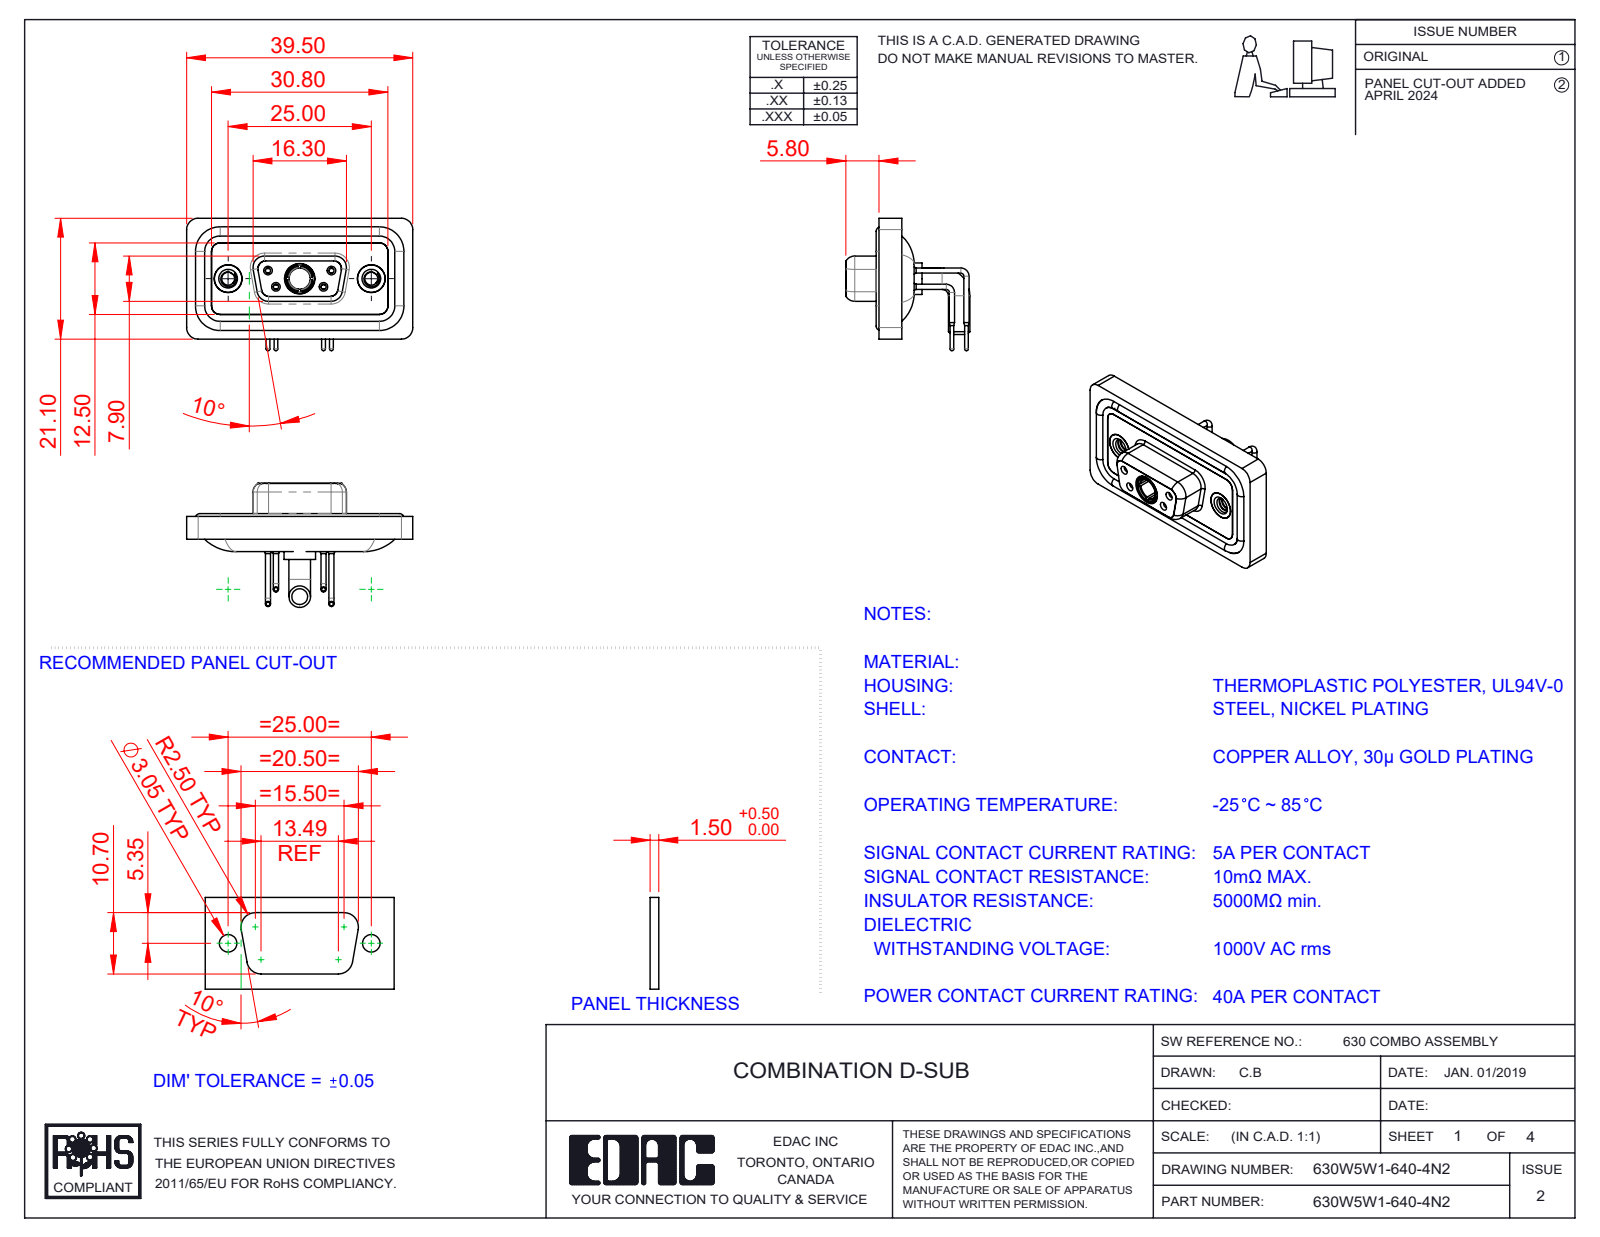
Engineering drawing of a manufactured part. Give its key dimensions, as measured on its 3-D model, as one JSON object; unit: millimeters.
{"part_name": "630Combo Contact Row 1_50 Contacts; 630Combo Shell Rear_09 Contacts; Power Socket_40A RA; 630Combo Waterproof Housing_09 Contacts (+5 more)", "step_written_by": "SolidWorks 2023 (CONFIG_CONTROL_DESIGN)", "units": "millimeters", "bodies": {"solids": 13, "faces": 676, "planar": 194, "cylindrical": 305, "other": 177}, "overall_size": [39.5, 23.12, 21.68], "volume_mm3": 4901, "surface_area_mm2": 7887, "round_holes": [[0.9, 4], [1.1, 4], [1.5, 4], [2, 4], [4.85, 3], [1.6, 2], [1.7, 2], [2.26, 2], [4, 2], [4.05, 2], [5, 2], [3.7, 1]], "round_bosses_or_shafts": [[1.6, 6], [0.9, 4], [0.65, 4], [4.95, 2], [4.8, 2], [3.75, 2], [5.5, 1], [5.2, 1]], "partial_cylinders_radius": [[1.5, 18], [2, 18], [1.35, 8], [1.6, 8], [0.25, 4], [0.5, 4], [0.6, 4], [0.65, 4]], "face_to_face_distances": [0.4, 1.8, 1.1, 2.9, 2.5, 1.6, 3.1, 2.1, 1.5, 0.5], "hole_center_spacings": [3.16, 5.72, 7.1, 12.5, 18.1, 4.39, 4.4, 8.31]}
